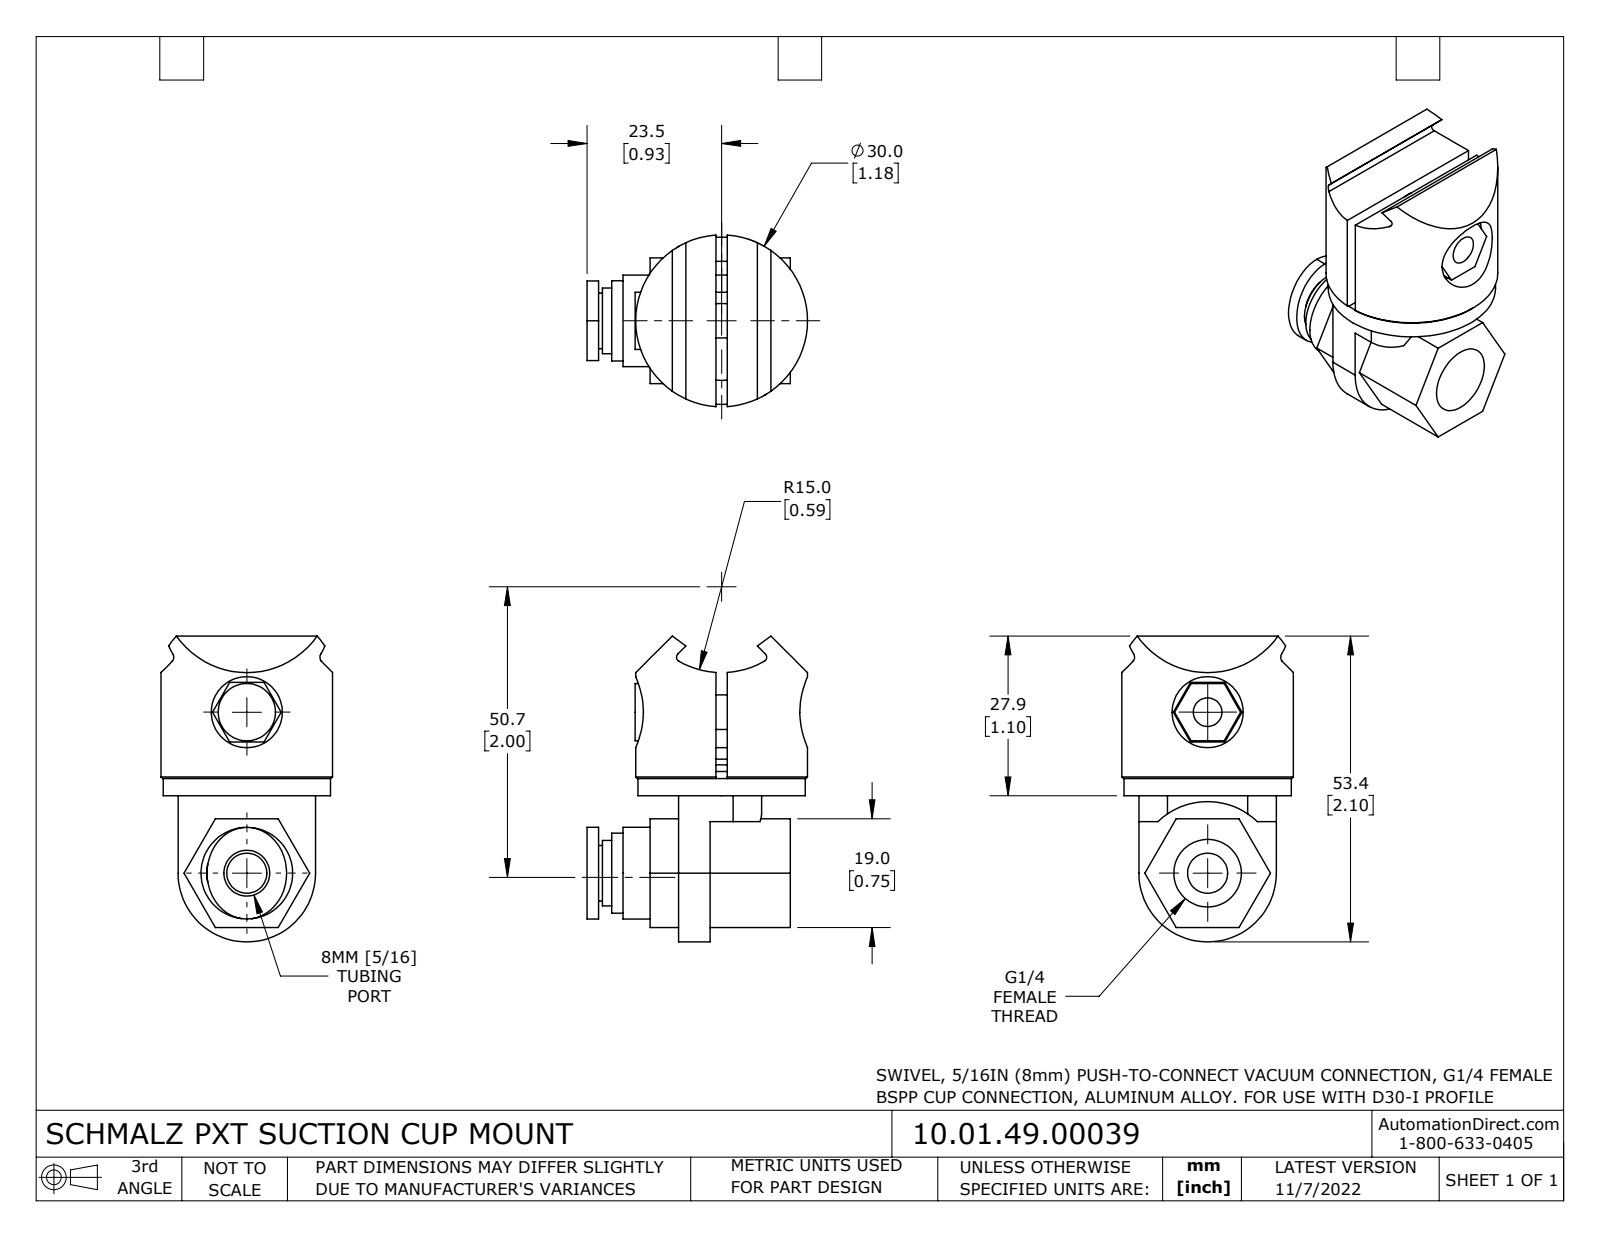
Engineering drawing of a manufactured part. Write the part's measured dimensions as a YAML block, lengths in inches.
part_name: "10.01.49.00039"
step_written_by: "SolidWorks 2021 (CONFIG_CONTROL_DESIGN)"
units: inches
bodies: {solids: 7, faces: 156, planar: 82, cylindrical: 62, other: 12}
overall_size: [2.102, 1.516, 1.178]
volume: 1.441
surface_area: 22.01
round_holes:
  - {diameter: 0.197, count: 1}
  - {diameter: 0.26, count: 1}
  - {diameter: 0.276, count: 1}
  - {diameter: 0.315, count: 1}
  - {diameter: 0.394, count: 1}
  - {diameter: 0.465, count: 1}
  - {diameter: 0.488, count: 1}
  - {diameter: 0.591, count: 1}
  - {diameter: 0.728, count: 1}
  - {diameter: 0.866, count: 1}
round_bosses_or_shafts:
  - {diameter: 1.181, count: 1}
  - {diameter: 1.15, count: 1}
  - {diameter: 0.819, count: 1}
  - {diameter: 0.689, count: 1}
  - {diameter: 0.63, count: 1}
  - {diameter: 0.551, count: 1}
  - {diameter: 0.545, count: 1}
  - {diameter: 0.451, count: 1}
partial_cylinders:
  - {radius: 0.031, count: 2}
  - {radius: 0.197, count: 2}
  - {radius: 0.472, count: 1}
  - {radius: 0.492, count: 1}
  - {radius: 0.591, count: 1}
face_to_face_distances: [0.118, 0.079, 0.748, 0.157, 0.433, 0.039, 0.276, 0.256, 0.335, 0.134]
hole_center_spacings: [1.106]
